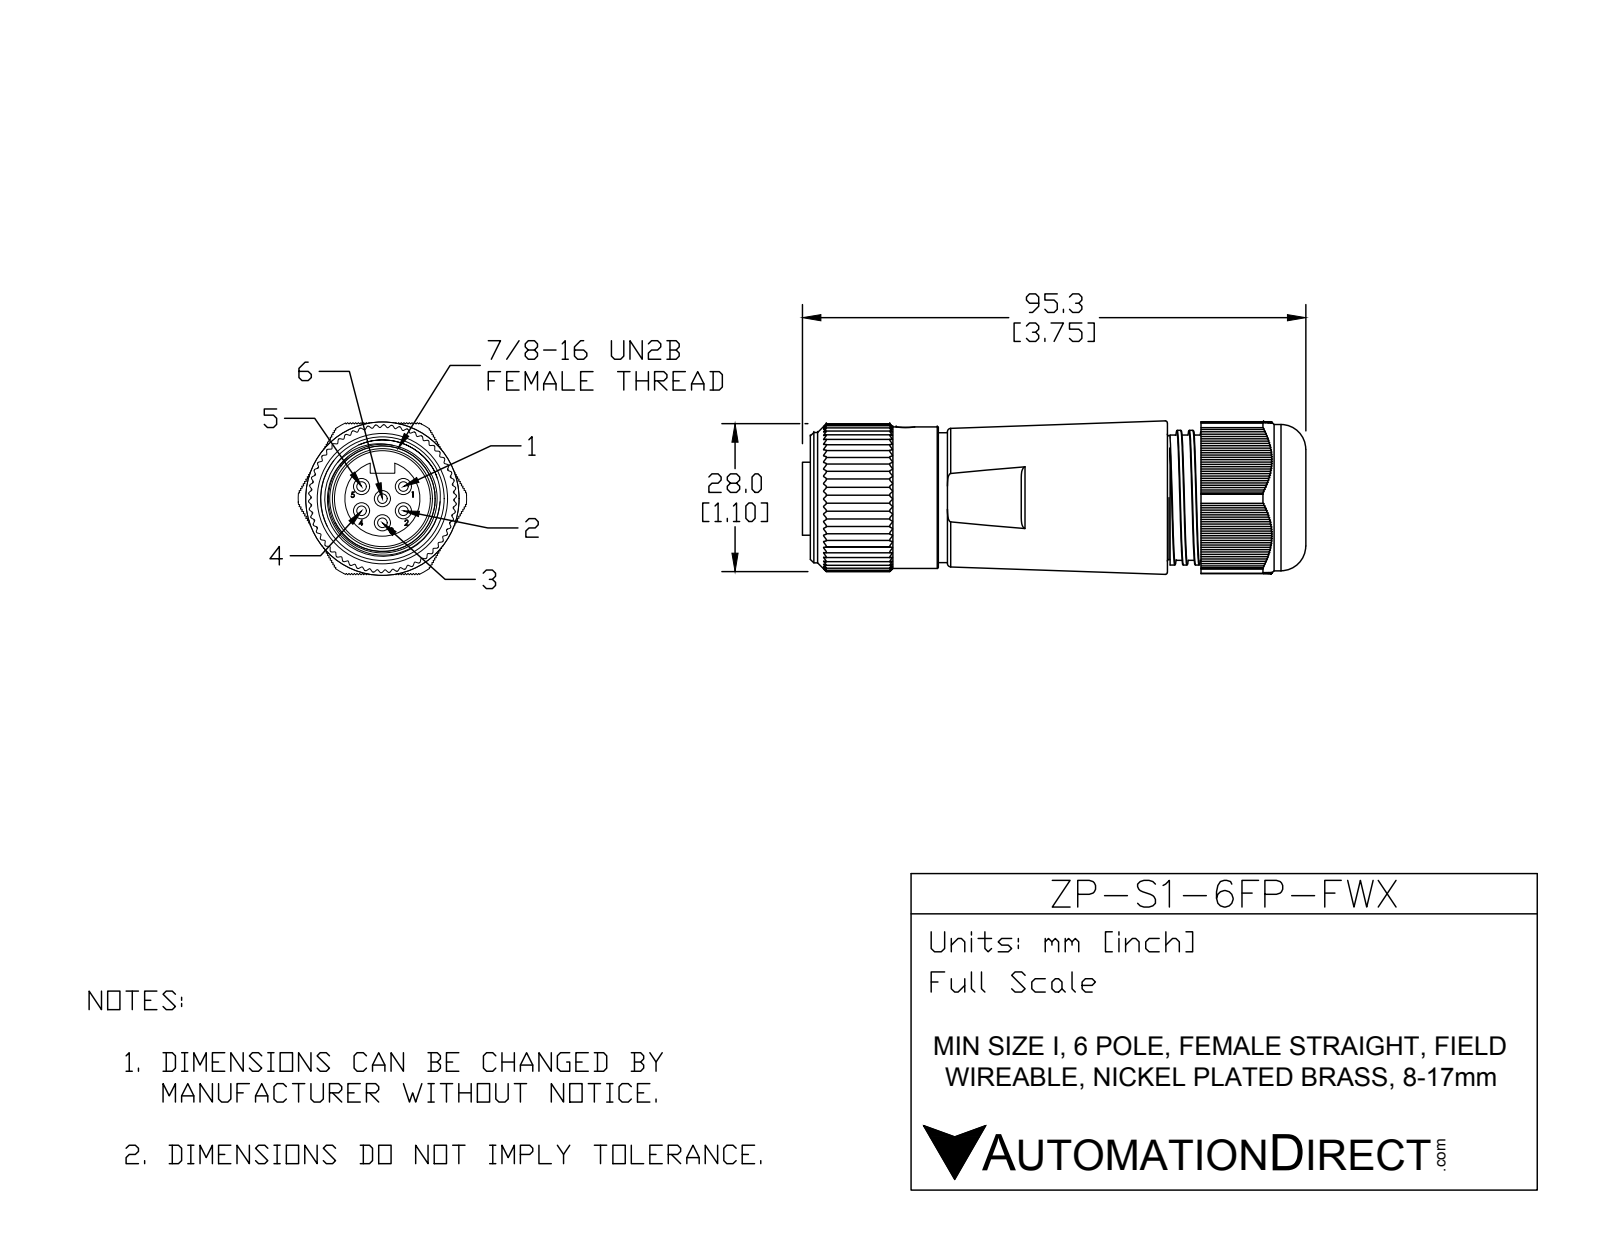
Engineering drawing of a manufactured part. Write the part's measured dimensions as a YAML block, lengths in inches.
part_name: "ZP-S1-6FP-FWX"
step_written_by: "SolidWorks 2015 (AUTOMOTIVE_DESIGN)"
units: inches
bodies: {solids: 4, faces: 898, planar: 523, cylindrical: 307, other: 68}
overall_size: [3.799, 1.256, 1.144]
volume: 3.053
surface_area: 25.57
round_holes:
  - {diameter: 0.12, count: 6}
  - {diameter: 0.138, count: 1}
  - {diameter: 0.68, count: 1}
  - {diameter: 0.81, count: 1}
  - {diameter: 0.849, count: 1}
  - {diameter: 0.953, count: 1}
  - {diameter: 1, count: 1}
round_bosses_or_shafts:
  - {diameter: 1.09, count: 1}
  - {diameter: 1.055, count: 1}
  - {diameter: 1.004, count: 1}
  - {diameter: 0.972, count: 1}
  - {diameter: 0.967, count: 1}
  - {diameter: 0.714, count: 1}
  - {diameter: 0.56, count: 1}
partial_cylinders:
  - {radius: 0.01, count: 165}
  - {radius: 0.551, count: 1}
  - {radius: 0.628, count: 1}
face_to_face_distances: [2.721, 0.042, 0.014, 0.028, 0.056, 0.083, 0.07, 0.346, 2.375, 0.808]
hole_center_spacings: [0.18, 0.311, 0.312, 0.36]
